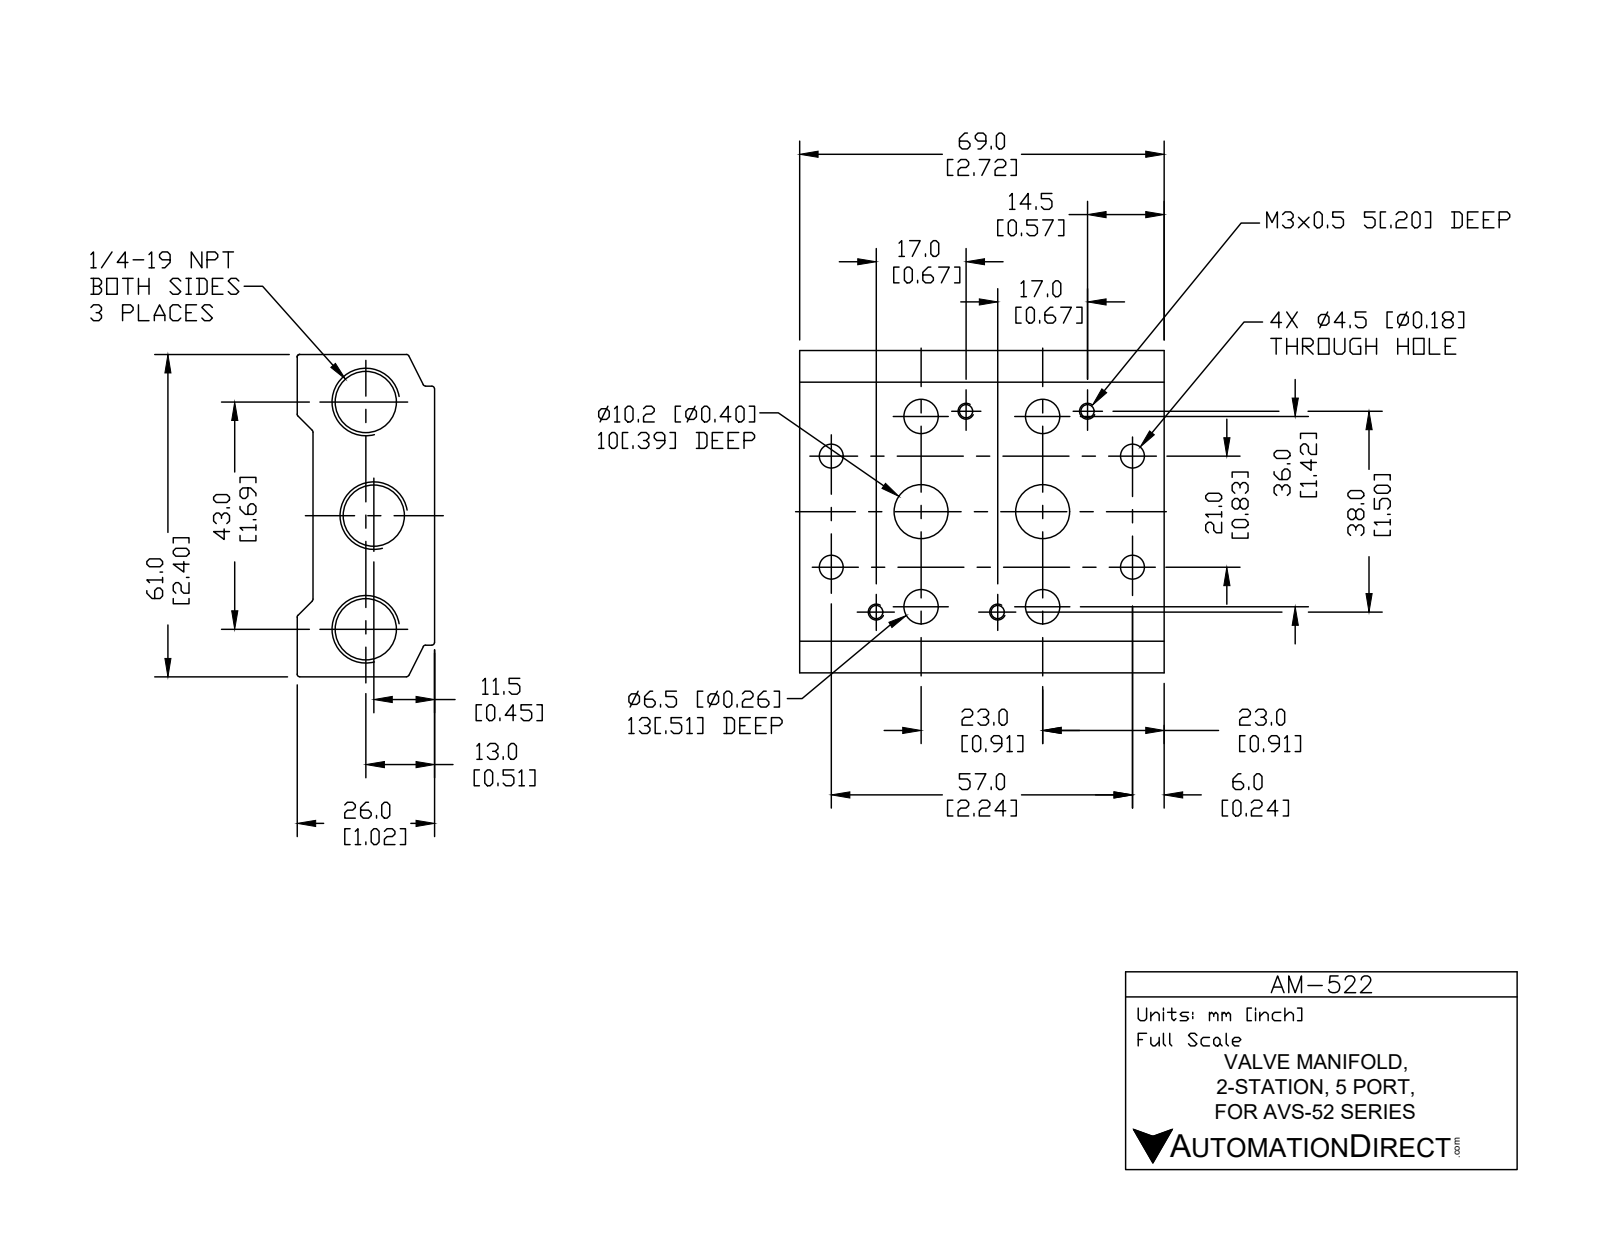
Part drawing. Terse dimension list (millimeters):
name: AM-522
written by: SolidWorks 2015 (CONFIG_CONTROL_DESIGN)
unit: mm
bodies: 1 solid, 89 faces (24 planar, 45 cylindrical, 20 other)
size: 69 × 61 × 26
volume: 73 480 mm³; area: 23 833 mm²
holes: 4× ⌀2.5, 4× ⌀4.5, 4× ⌀6.5, 3× ⌀11.13, 2× ⌀10.2
rounds: 11× R0.5
face distances: 23, 61, 3, 26, 69, 10.02, 58.98, 6, 55, 48.96
hole spacings: 23, 8.56, 18, 18.58, 19.98, 20.81, 29.21, 33.19
